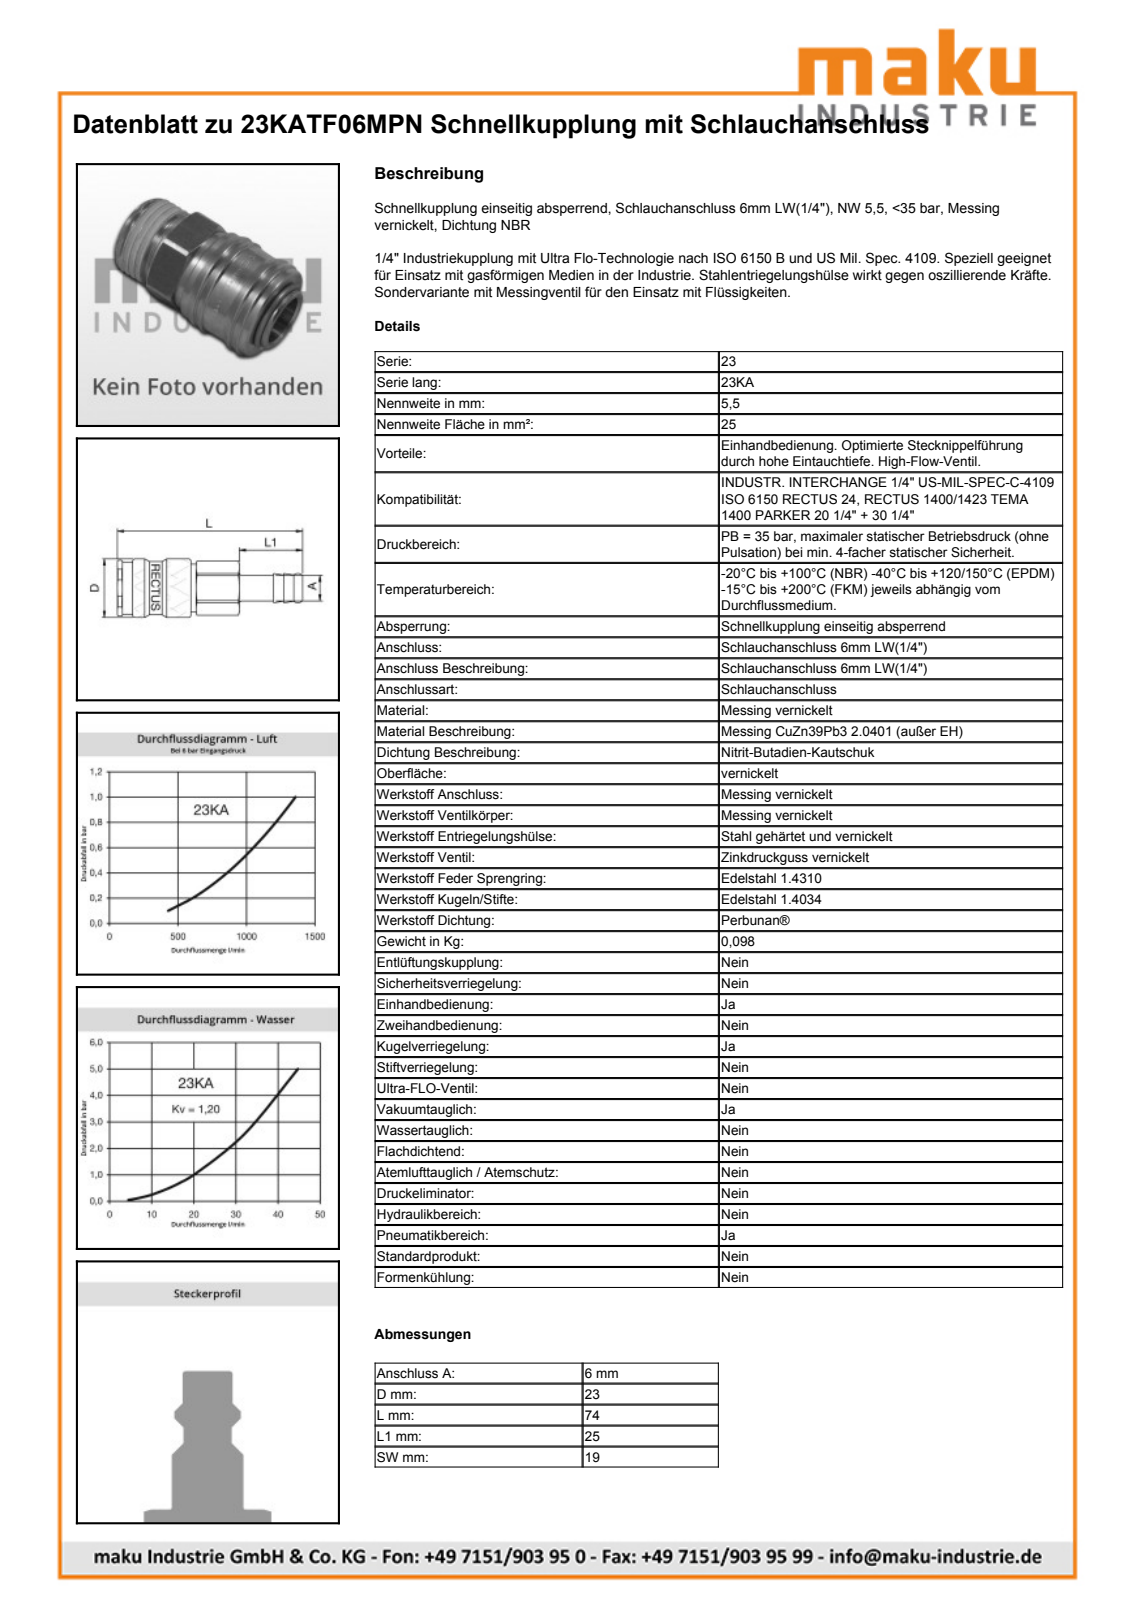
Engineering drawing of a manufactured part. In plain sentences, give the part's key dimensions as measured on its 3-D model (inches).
The part is named "D109358". Its 3-D file was written by "Autodesk Inventor 2013 (AUTOMOTIVE_DESIGN)". It is 2 solids with 543 faces: 170 planar, 67 cylindrical and 306 other. Overall it measures 2.878 by 0.911 by 0.911 inches. Its volume is 1.009 cubic inches and its surface area 11.77 square inches. Round holes: 1 of diameter 0.679, 1 of diameter 0.762. Round bosses or shafts: 1 of diameter 0.911, 1 of diameter 0.827, 1 of diameter 0.819, 1 of diameter 0.811, 1 of diameter 0.746, 1 of diameter 0.63, 1 of diameter 0.24, 1 of diameter 0.181. Partial cylindrical surfaces (rounded edges, fillets, slot ends): 1 of radius 0.307, 1 of radius 0.421, 1 of radius 0.433. The main face-to-face distances are 0.748, 1.894, 0.949, 0.945, 0.201, 1.146, 1.142, 0.394, 0.193, 0.752.
